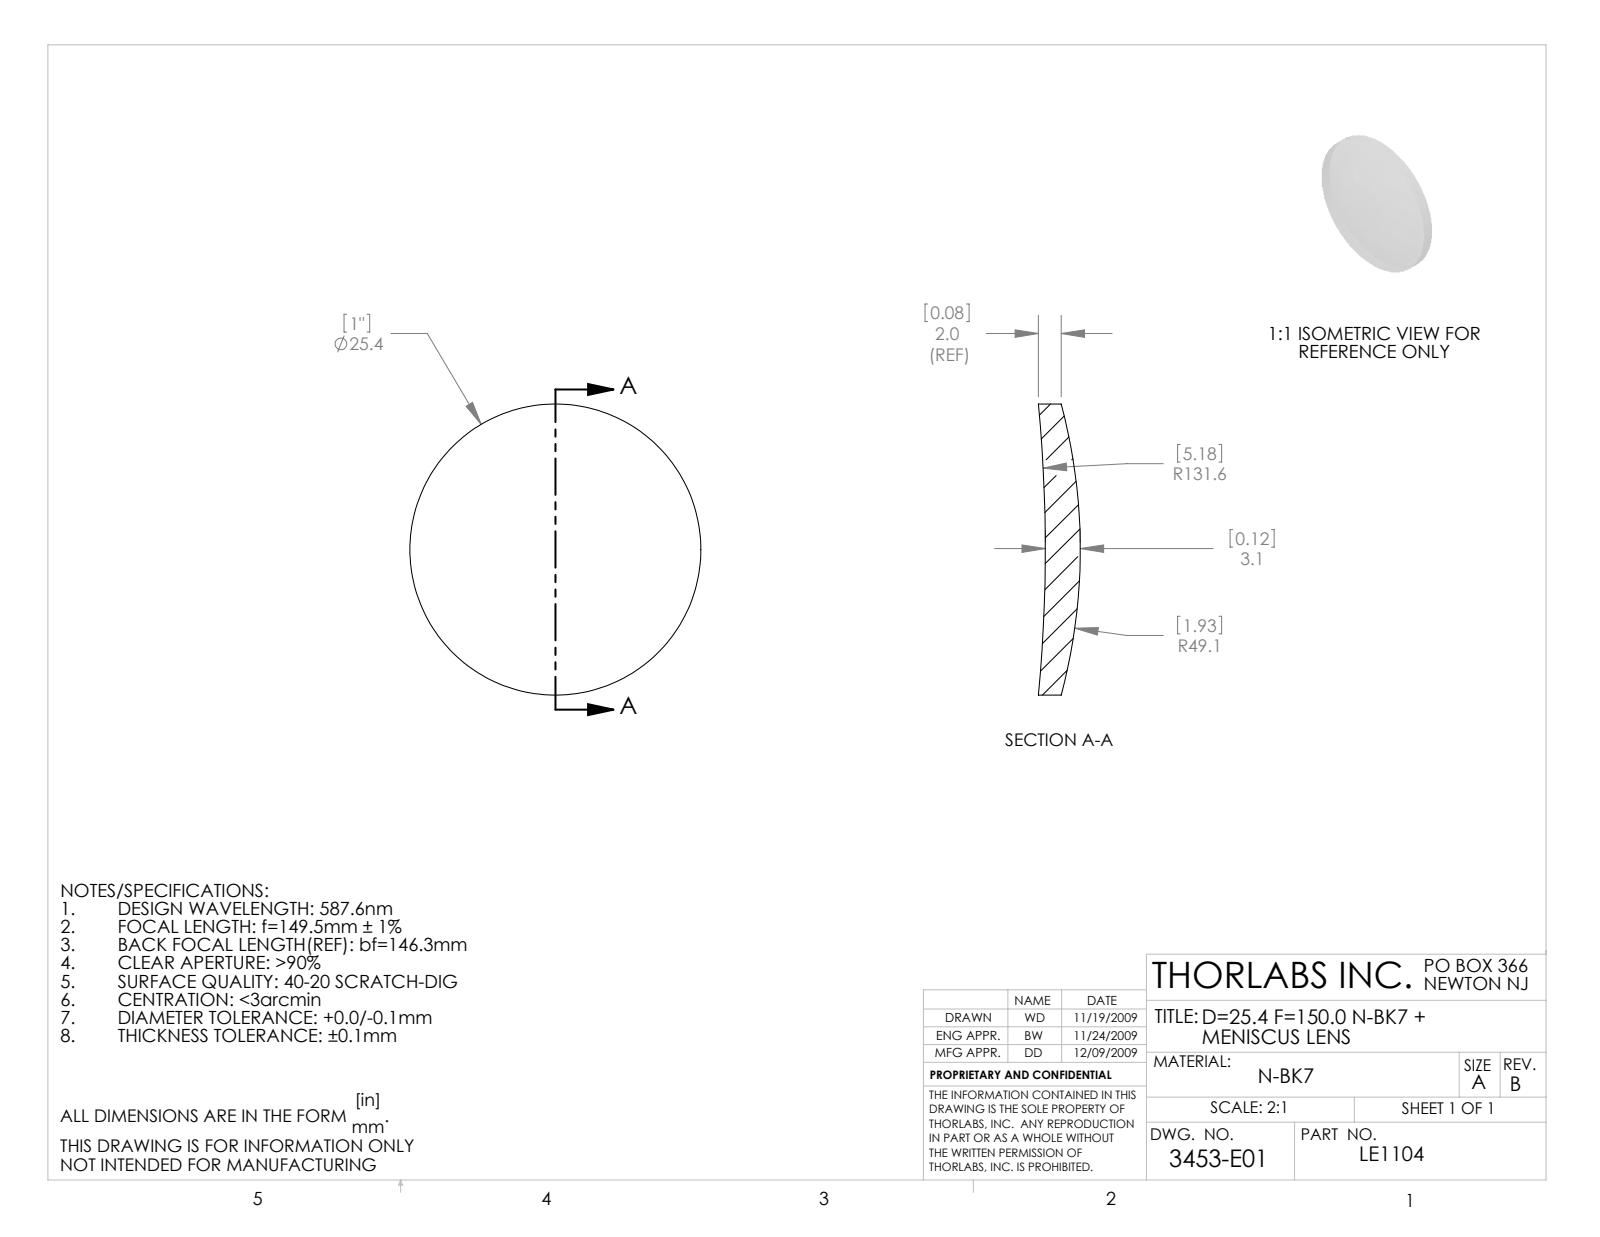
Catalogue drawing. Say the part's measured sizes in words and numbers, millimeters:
The part is named "3453-E0W". Its 3-D file was written by "SolidWorks 2009 (AUTOMOTIVE_DESIGN)". It is 1 solid with 6 faces: 0 planar, 2 cylindrical and 4 other. Overall it measures 25.4 by 25.4 by 3.66 millimeters. Its volume is 1 280 cubic millimeters and its surface area 1 182 square millimeters. Round bosses or shafts: 1 of diameter 25.4.
